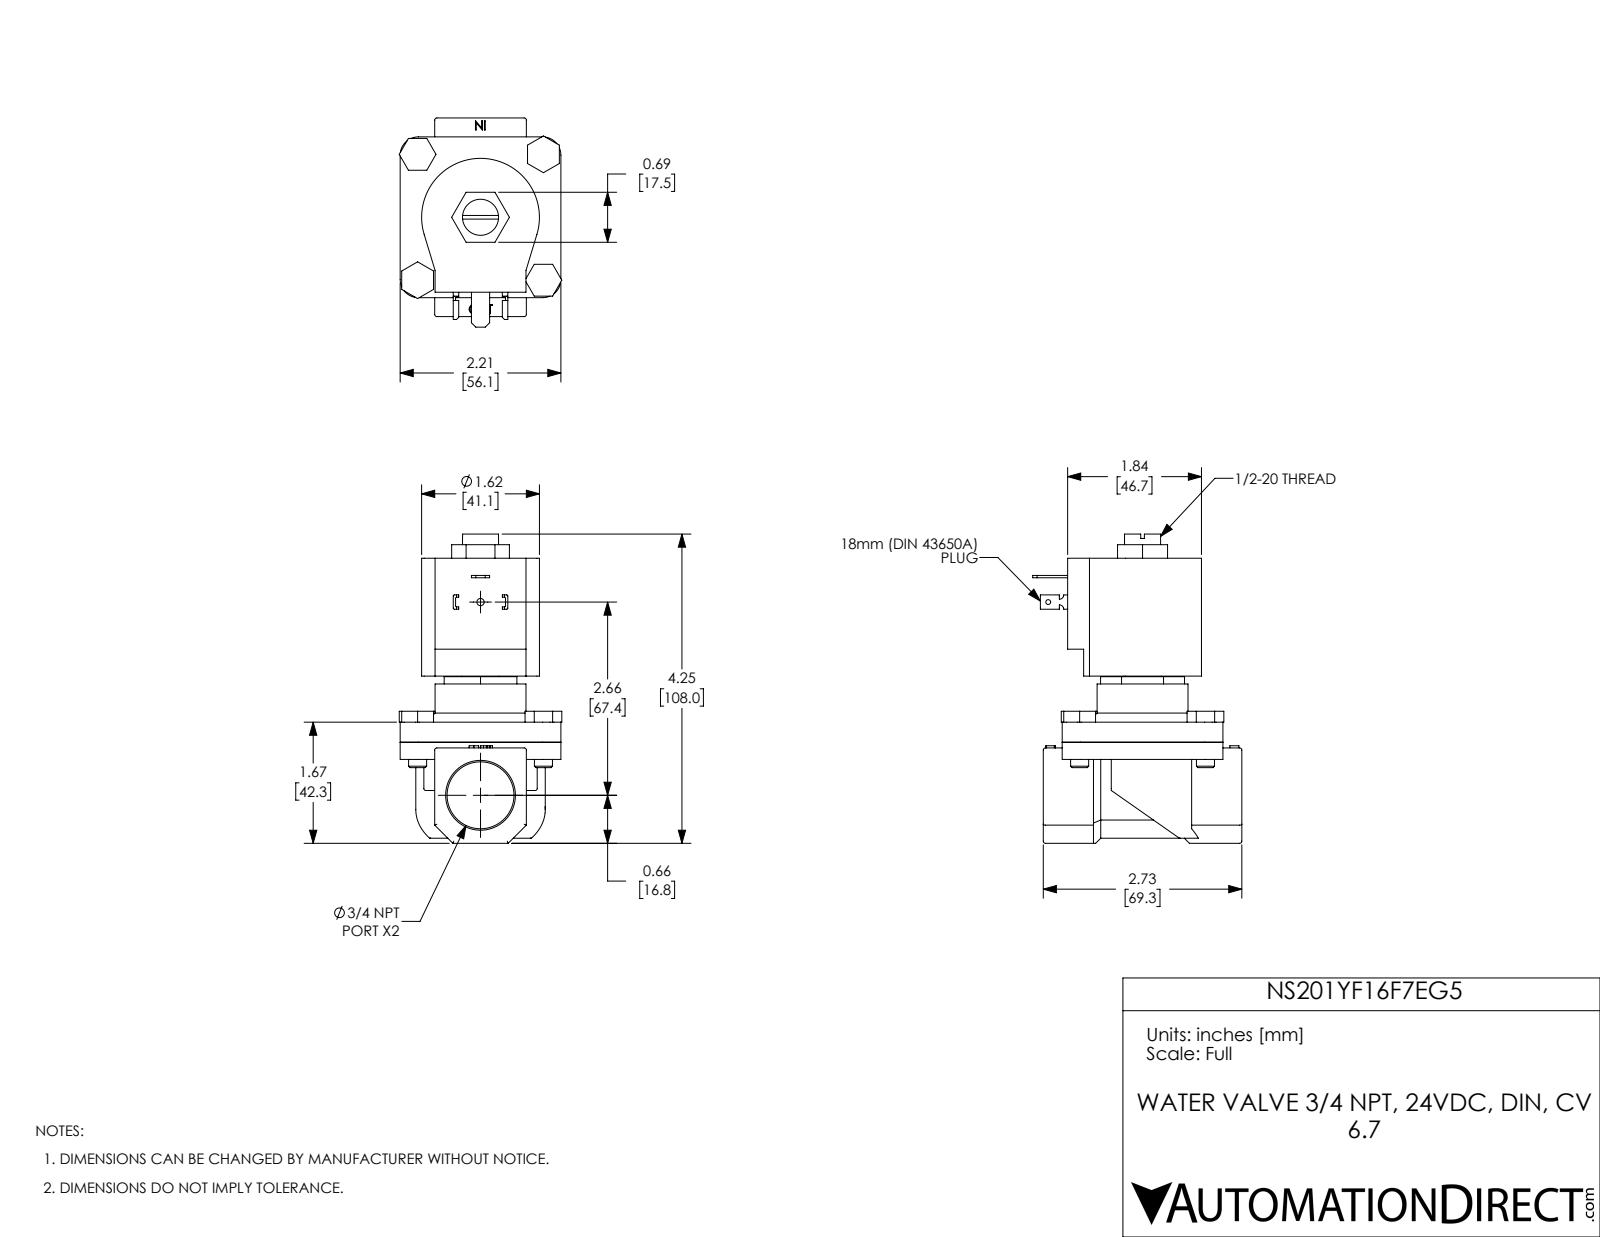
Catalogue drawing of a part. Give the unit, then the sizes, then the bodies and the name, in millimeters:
Units: millimetres
Overall size (bounding box): 108 × 73 × 56.8
Round holes (diameter × count): ⌀6.4 ×4, ⌀1.7 ×1, ⌀2.5 ×1, ⌀12.6 ×1, ⌀13 ×1, ⌀23.4 ×1, ⌀29.3 ×1
Round bosses / shafts (diameter × count): ⌀6.3 ×4, ⌀31.8 ×1
Partial cylindrical surfaces — rounded edges, fillets, slot ends (radius × count): R0.8 ×15, R0.4 ×8, R6.4 ×4, R1.5 ×2, R20.6 ×1, R22.6 ×1
Main face-to-face distances: 7, 64.2, 57.2, 12.1, 44.1, 56.1, 6, 13, 70.2, 6.6
Hole centre spacings: 31.1, 43.9, 62.1, 67.5
Volume: 169 600 mm³ · Surface area: 43 410 mm²
Bodies: 11 solids, 332 faces (198 planar, 99 cylindrical, 35 other)
Part name (STEP PRODUCT): NS201YF16F7EG5
STEP written by: SolidWorks 2017 (AUTOMOTIVE_DESIGN)
